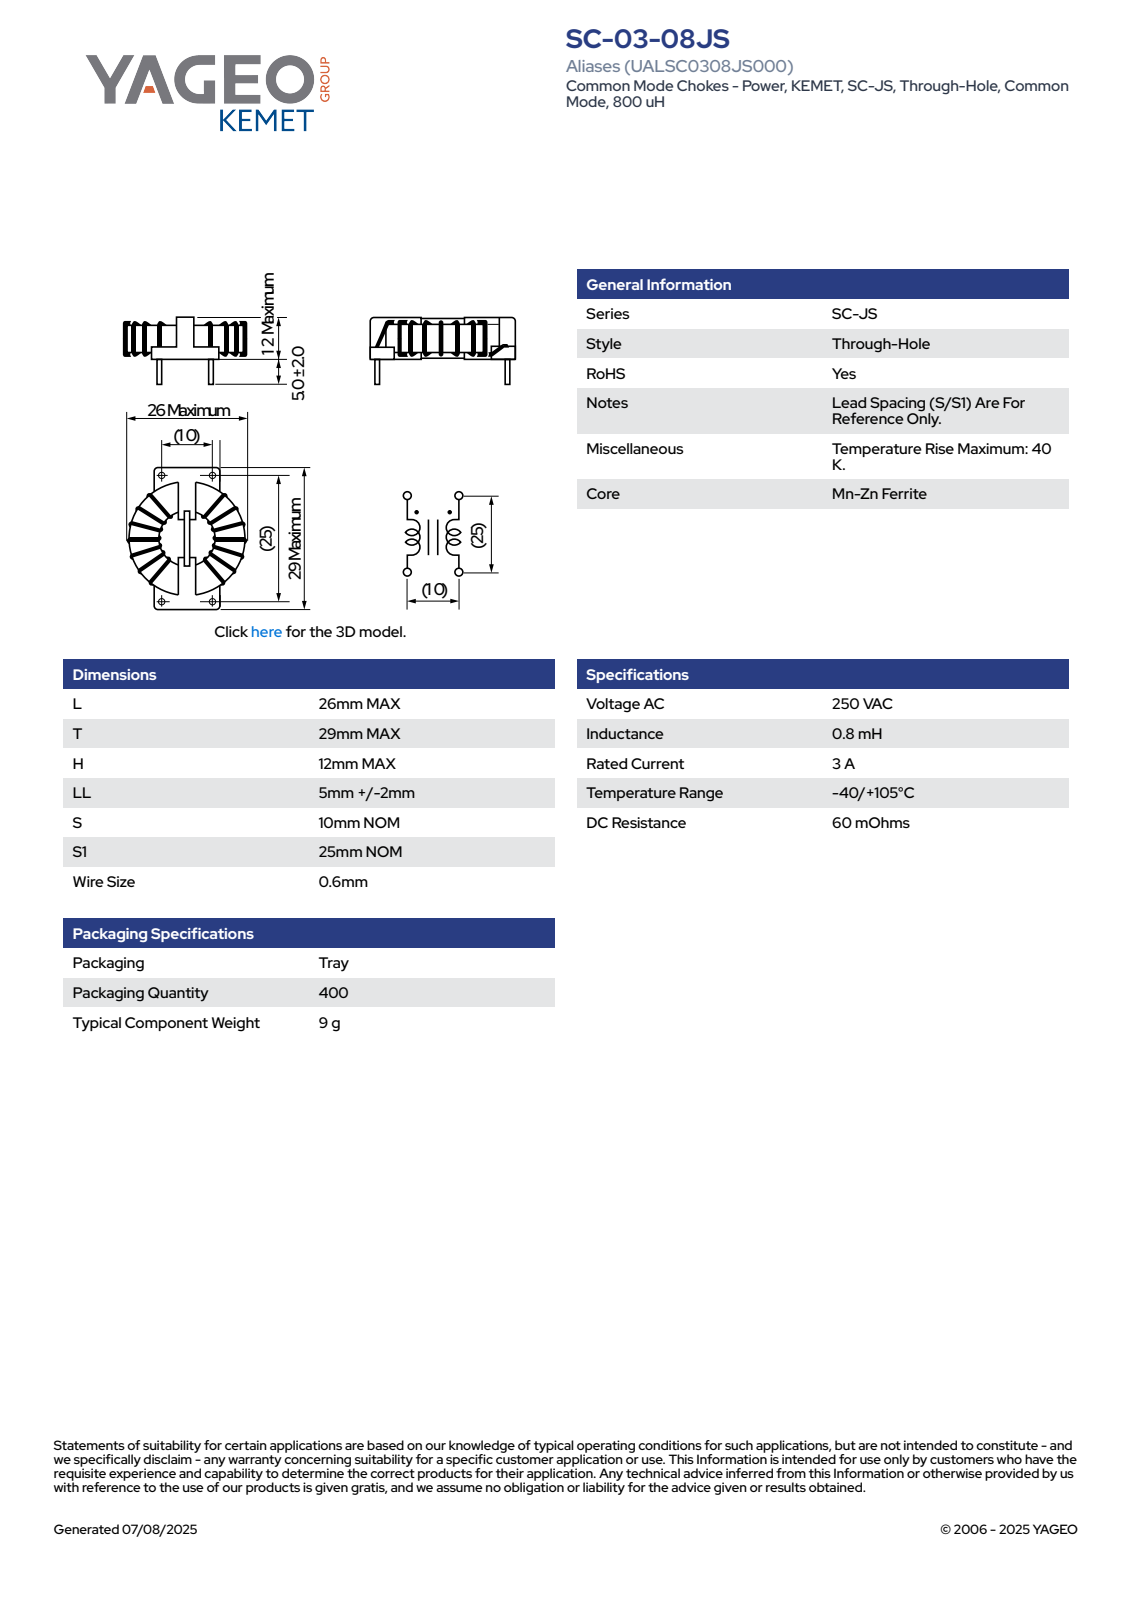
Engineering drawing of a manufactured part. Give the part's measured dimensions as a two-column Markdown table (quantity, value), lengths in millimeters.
| quantity | value |
| --- | --- |
| part name | SC-03-08JS |
| STEP written by | SolidWorks 2018 (AUTOMOTIVE_DESIGN) |
| units | millimeters |
| bodies | 1 solid, 341 faces (142 planar, 127 cylindrical, 72 other) |
| overall size | 29 × 26 × 17 |
| volume | 4 146 mm³ |
| surface area | 3 362 mm² |
| round holes (diameter × count) | 0.7 × 4, 1.6 × 2 |
| round bosses / shafts (diameter × count) | 0.6 × 10, 1.5 × 2 |
| partial cylindrical surfaces (radius × count) | 0.3 × 16, 0.2 × 14, 0.7 × 4, 1.5 × 4, 4 × 1, 4.97 × 1, 5.38 × 1, 5.47 × 1 |
| main face-to-face distances | 2.15, 1.05, 8.62, 1.4, 10.02, 3.2, 1.1, 1.15, 1, 4.15 |
| hole center spacings | 5, 25.5, 25, 10, 26.93 |
